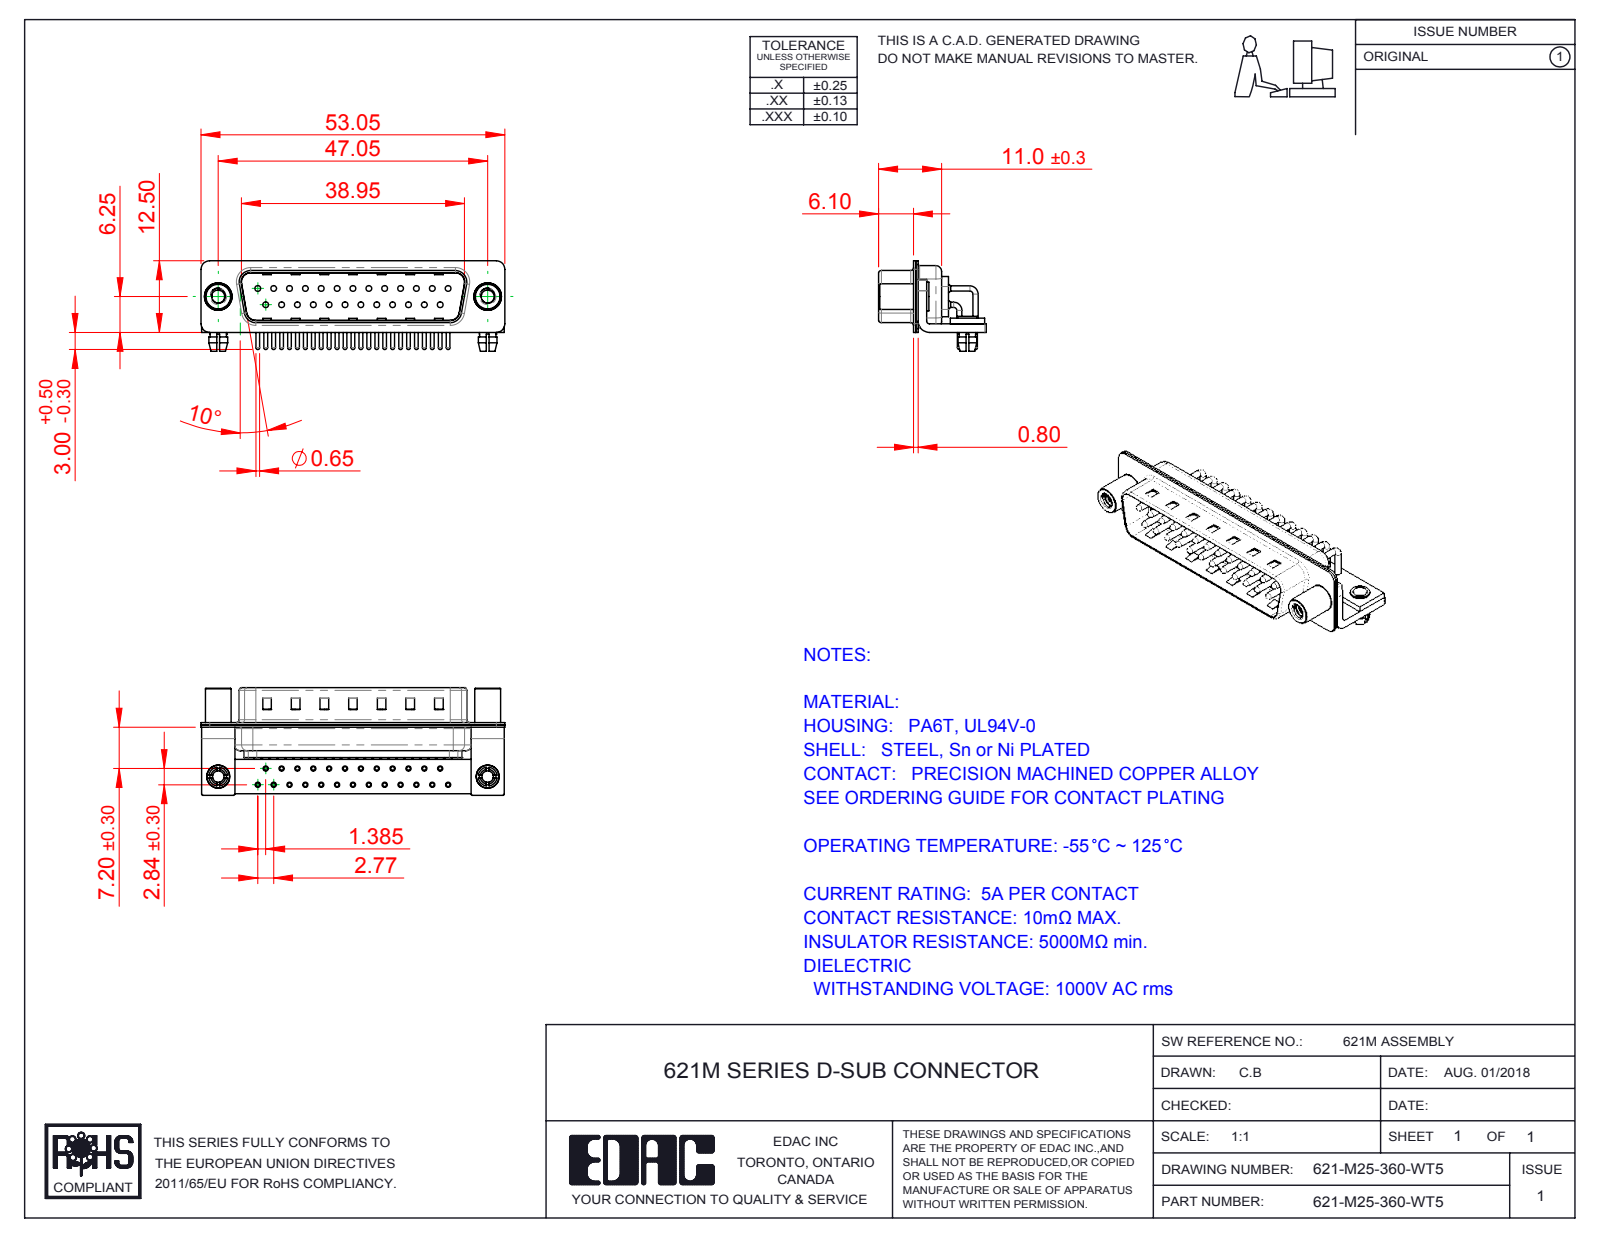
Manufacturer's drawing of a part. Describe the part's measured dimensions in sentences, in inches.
The part is named "621-M25-360-WT5; 621M Shell Front_25 Contacts; 621M Housing_25 Contacts; 621M Board Lock (+6 more)". Its 3-D file was written by "SolidWorks 2016 (CONFIG_CONTROL_DESIGN)". It is 35 solids with 3368 faces: 1847 planar, 1183 cylindrical and 338 other. Overall it measures 2.089 by 0.74 by 0.622 inches. Its volume is 0.217 cubic inches and its surface area 14.65 square inches. Round holes: 27 of diameter 0.079, 25 of diameter 0.035, 25 of diameter 0.039, 25 of diameter 0.067, 2 of diameter 0.089, 2 of diameter 0.098, 2 of diameter 0.126, 2 of diameter 0.157, 2 of diameter 0.189. Round bosses or shafts: 33 of diameter 0.035, 25 of diameter 0.059, 25 of diameter 0.026, 2 of diameter 0.197, 2 of diameter 0.193, 2 of diameter 0.177, 2 of diameter 0.157, 2 of diameter 0.134. Partial cylindrical surfaces (rounded edges, fillets, slot ends): 25 of radius 0.04, 16 of radius 0.01, 16 of radius 0.059, 13 of radius 0.079, 9 of radius 0.02, 8 of radius 0.063, 4 of radius 0.024, 4 of radius 0.026. The main face-to-face distances are 0.016, 0.033, 0.049, 0.059, 0.376, 0.031, 0.409, 0.327, 0.039, 0.075. The hole center spacings are 0.124, 0.109, 0.327, 0.218, 0.436, 0.545, 0.198, 0.654.
